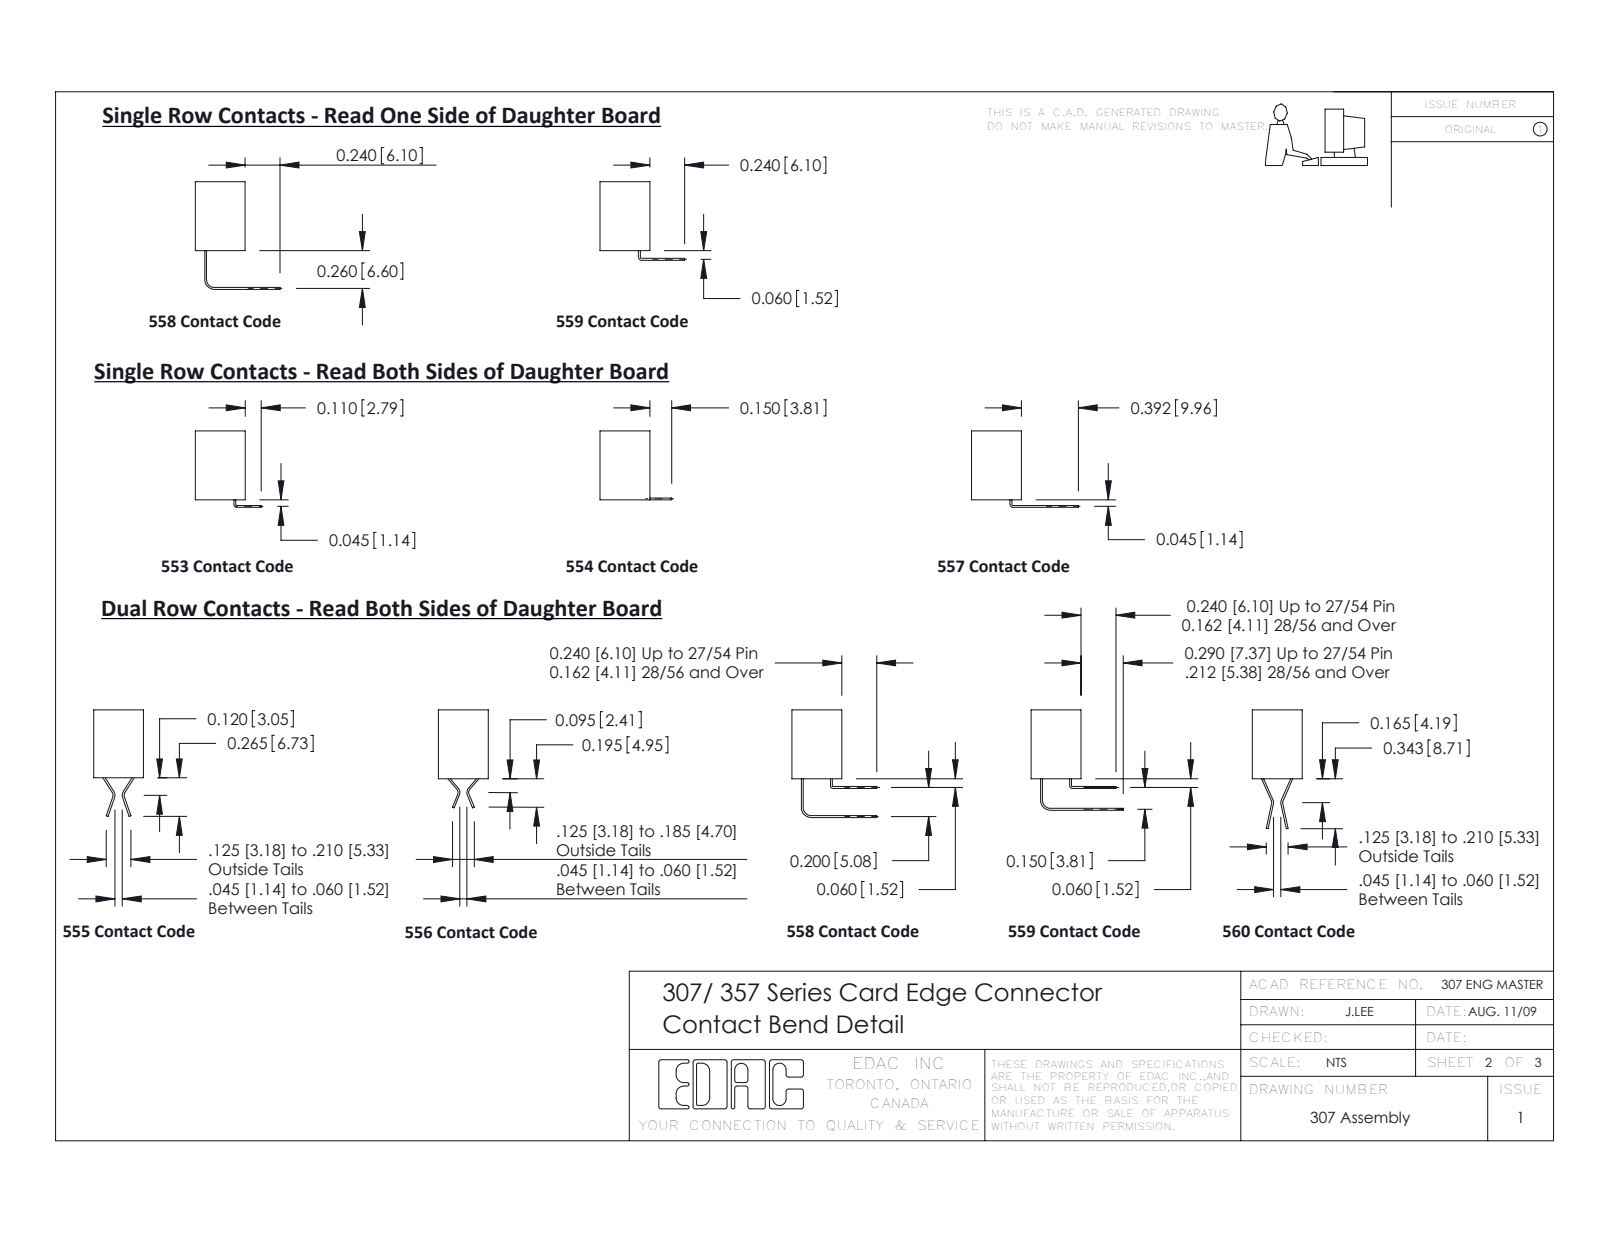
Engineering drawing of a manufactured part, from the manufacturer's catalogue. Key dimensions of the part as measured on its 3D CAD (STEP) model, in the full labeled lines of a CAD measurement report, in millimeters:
Part name (STEP PRODUCT): 307-290-001_558 - 2 (Single); 307 Part_.128 Dia Mounting Holes; 357-006-458-102
STEP written by: SolidWorks 2020 (CONFIG_CONTROL_DESIGN)
Units: millimetres
Bodies: 7 solids, 485 faces (304 planar, 167 cylindrical, 14 other)
Overall size (bounding box): 46.8 × 18.8 × 14.8
Volume: 2 930 mm³ · Surface area: 3 925 mm²
Round holes (diameter × count): ⌀4 ×2
Partial cylindrical surfaces — rounded edges, fillets, slot ends (radius × count): R0.5 ×35, R0.3 ×22, R0.2 ×6, R0.6 ×6, R0.8 ×6, R0.7 ×3, R1.2 ×2, R0.3 ×1
Main face-to-face distances: 8.7, 0.3, 4, 7.1, 1.7, 6.2, 3.6, 5.1, 6.7, 2
Hole centre spacings: 38.9
